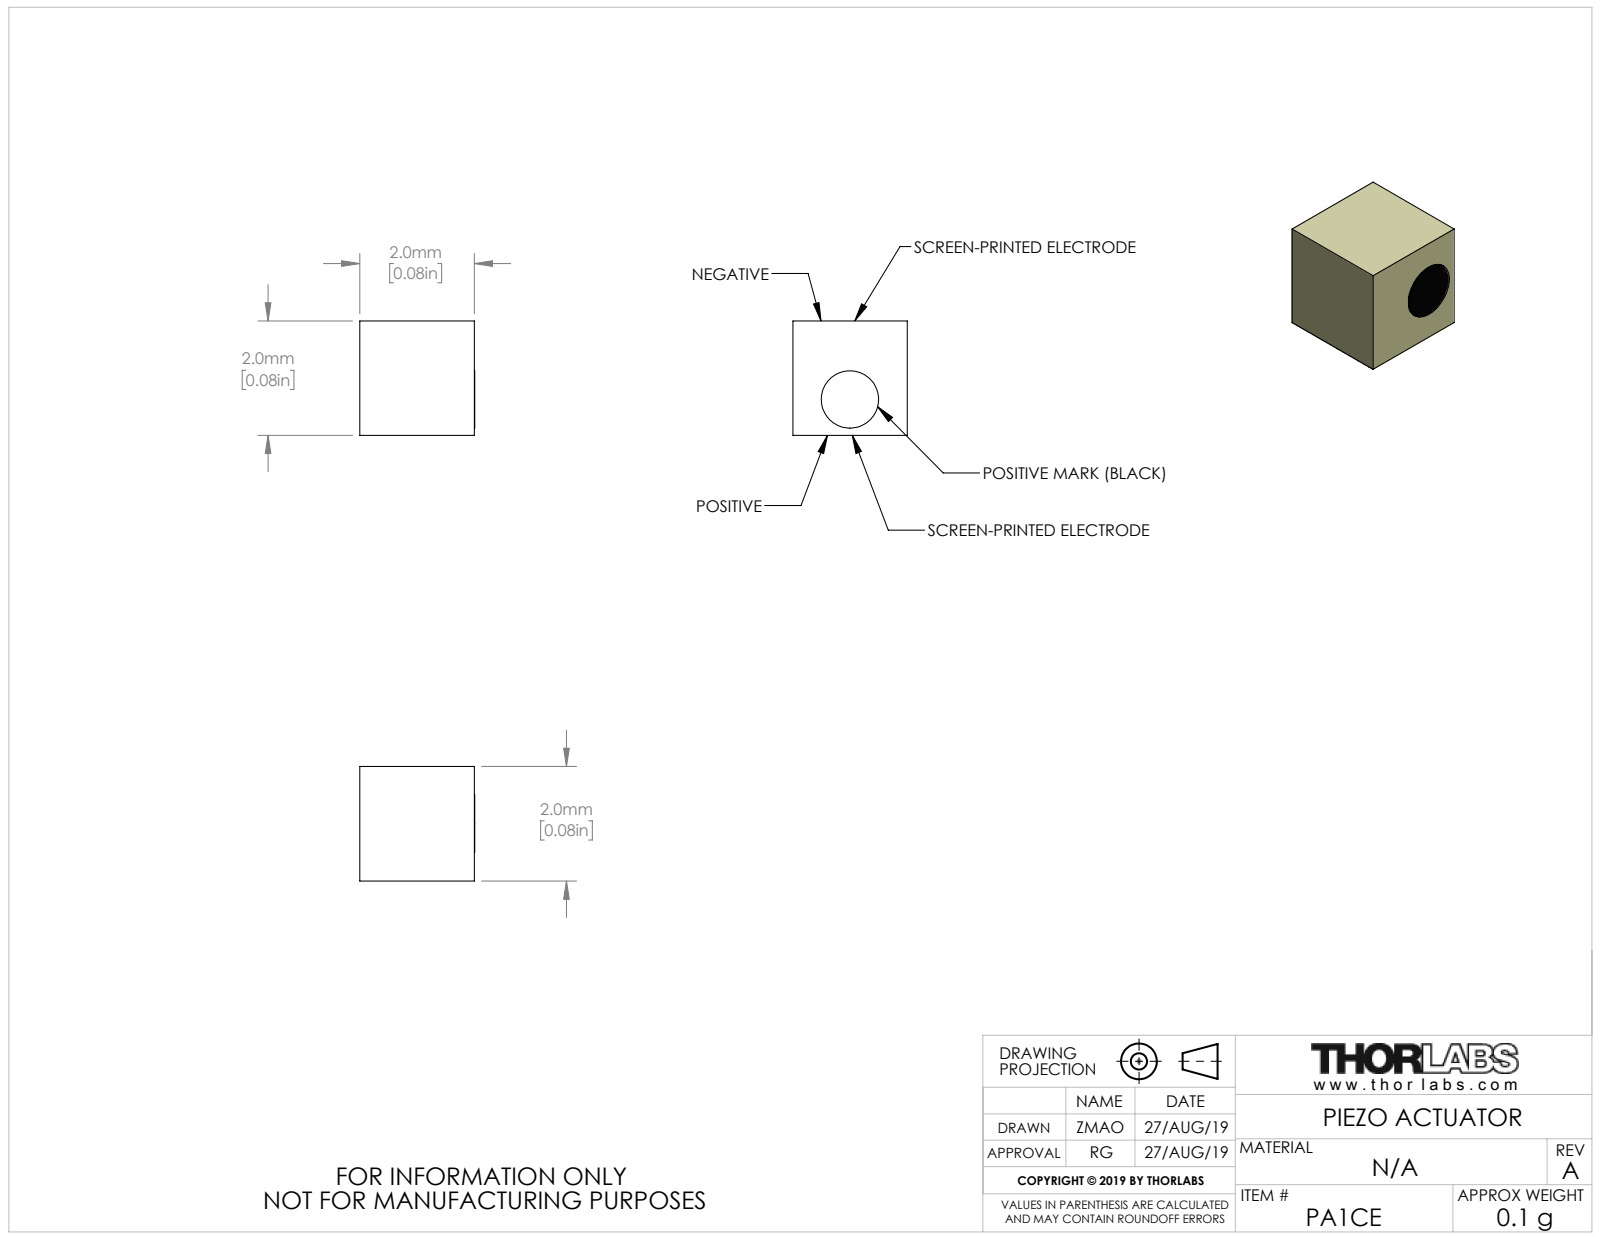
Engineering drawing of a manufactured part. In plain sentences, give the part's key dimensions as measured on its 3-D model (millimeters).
The part is named "CTN014514". Its 3-D file was written by "SolidWorks 2018 (AUTOMOTIVE_DESIGN)". It is 1 solid with 9 faces: 7 planar, 2 cylindrical and 0 other. Overall it measures 2.01 by 2 by 2 millimeters. Its volume is 8 cubic millimeters and its surface area 24 square millimeters. Round bosses or shafts: 1 of diameter 1. The main face-to-face distances are 2, 2.01.
